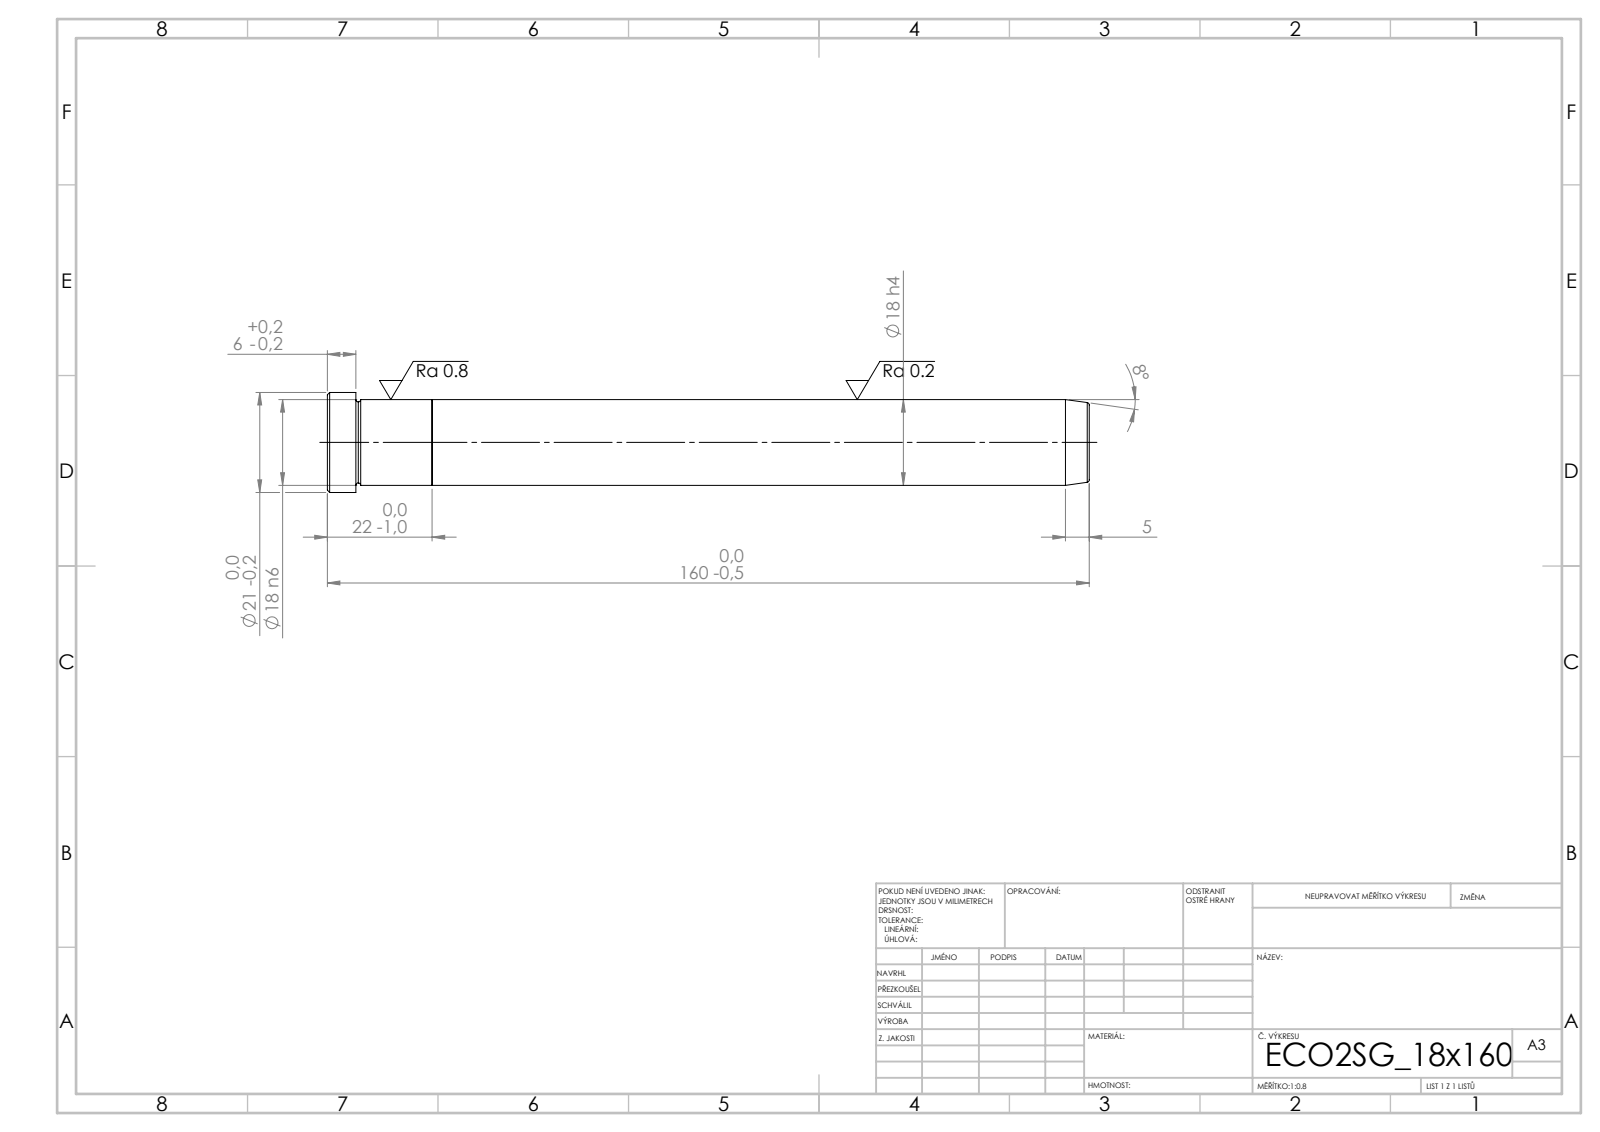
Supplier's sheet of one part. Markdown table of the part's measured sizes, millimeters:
| quantity | value |
| --- | --- |
| STEP written by | SolidWorks 2019 (CONFIG_CONTROL_DESIGN) |
| units | millimeters |
| bodies | 2 solids, 21 faces (5 planar, 6 cylindrical, 10 other) |
| overall size | 160 × 21 × 21 |
| volume | 41 138 mm³ |
| surface area | 10 261 mm² |
| round bosses / shafts (diameter × count) | 21 × 1, 18 × 1 |
| main face-to-face distances | 22, 138, 160, 154, 16, 6 |
